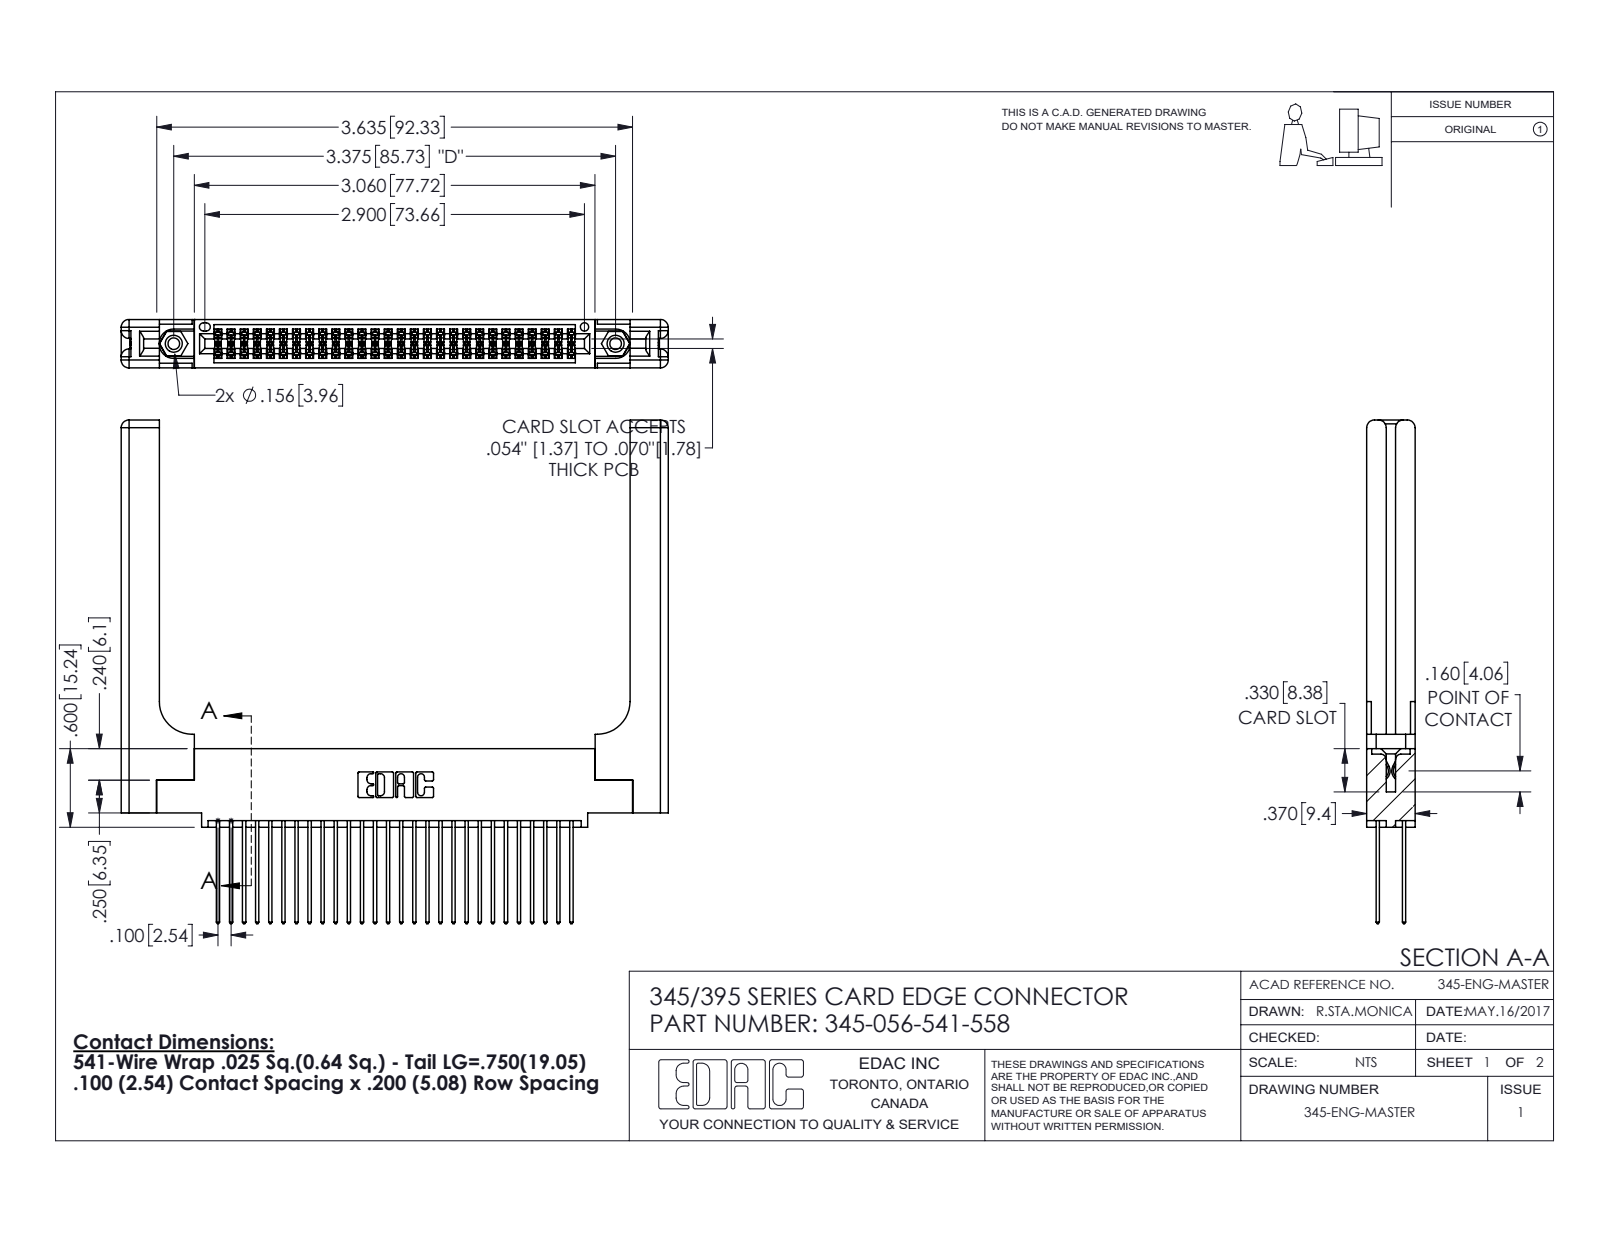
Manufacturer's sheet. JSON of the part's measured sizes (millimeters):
{"part_name": "345-250-001_345-250-001-102; 345-292-001_345-293-141; 345-220-058_345-220-058; 345 Part_0.110 Offset - 0.156 Dia-TH (+1 more)", "step_written_by": "SolidWorks 2016 (CONFIG_CONTROL_DESIGN)", "units": "millimeters", "bodies": {"solids": 61, "faces": 3186, "planar": 2080, "cylindrical": 1046, "other": 60}, "overall_size": [106.1, 97.7, 9.4], "volume_mm3": 18910, "surface_area_mm2": 21810, "round_holes": [[2.3, 2], [3.2, 2], [4, 2], [1.6, 1]], "round_bosses_or_shafts": [[3.9, 2]], "partial_cylinders_radius": [[0.2, 84], [0.3, 56], [0.3, 22], [1.5, 16], [0.2, 6], [0.8, 6], [0.7, 3], [0.4, 2]], "face_to_face_distances": [1.8, 7.6, 9.4, 2.5, 6.9, 0.6, 5.1, 5.7, 3.8, 3.8], "hole_center_spacings": [6.9, 79.8, 85.7]}
